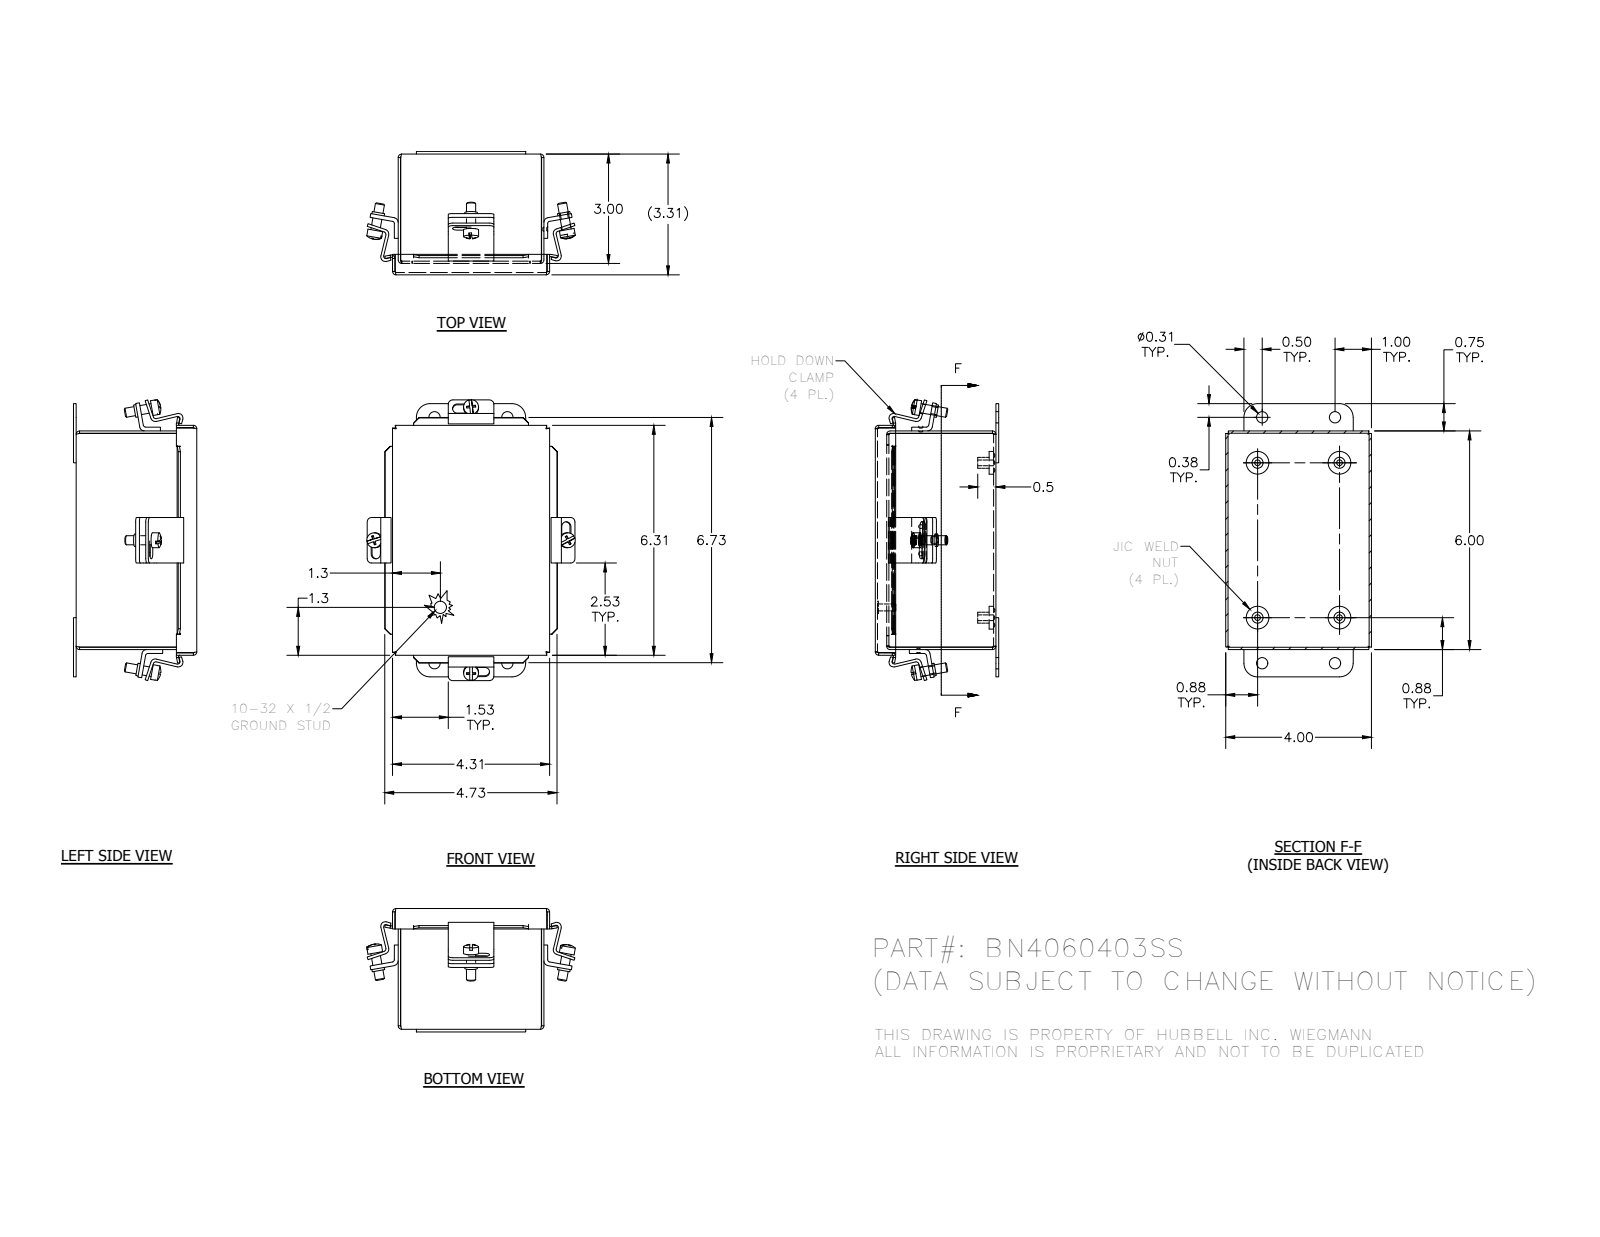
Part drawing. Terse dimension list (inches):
name: C2002_1; HFW3883_1; BN4060403SSBKP_1; BN40604SSLID_1 (+5 more)
written by: SolidWorks 2014 (AUTOMOTIVE_DESIGN)
unit: in
bodies: 21 solids, 589 faces (287 planar, 200 cylindrical, 102 other)
size: 7.712 × 5.724 × 3.388
volume: 10.2 in³; area: 317.4 in²
holes: 6× ⌀0.11, 4× ⌀0.156, 4× ⌀0.196, 4× ⌀0.31
bosses: 4× ⌀0.625, 4× ⌀0.41, 4× ⌀0.344, 4× ⌀0.3, 4× ⌀0.25, 1× ⌀0.337, 1× ⌀0.19
rounds: 16× R0.031, 16× R0.094, 16× R0.125, 12× R0.063, 12× R0.126, 8× R0.133, 4× R0.375
face distances: 0.063, 3.25, 3.937, 3.313, 3.187, 5.937, 4, 3.875, 0.075, 0.155
hole spacings: 1.256, 5.502, 0.75, 0.063, 0.753, 2, 2.25, 2.465
